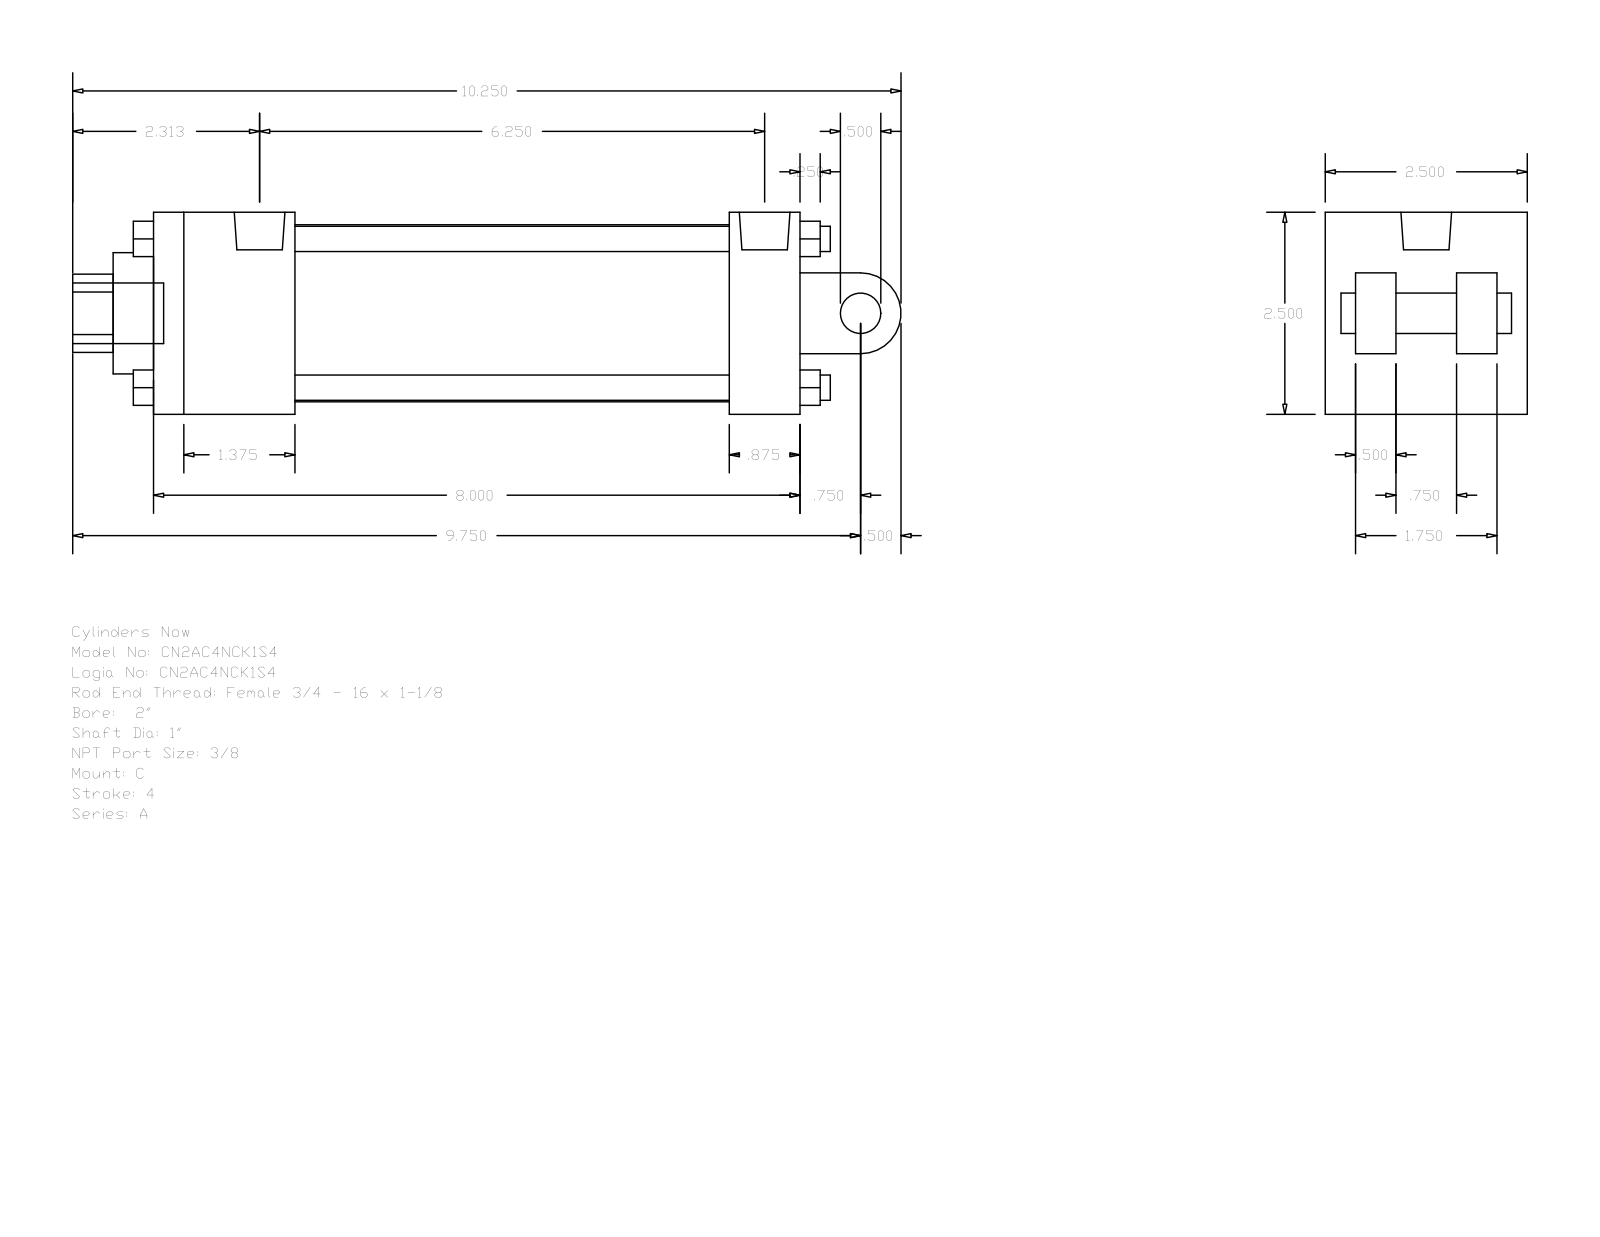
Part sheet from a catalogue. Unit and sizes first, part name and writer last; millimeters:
Units: millimetres
Overall size (bounding box): 260.35 × 63.5 × 63.5
Round holes (diameter × count): ⌀5.56 ×2, ⌀15.93 ×1, ⌀25.4 ×1, ⌀38.1 ×1, ⌀55.63 ×1
Round bosses / shafts (diameter × count): ⌀7.94 ×4, ⌀5.56 ×2, ⌀19.05 ×1, ⌀15.93 ×1, ⌀12.7 ×1
Partial cylindrical surfaces — rounded edges, fillets, slot ends (radius × count): R12.29 ×1, R12.7 ×1
Main face-to-face distances: 63.5, 22.22, 203.2, 44.45, 12.7, 9.52, 41.28, 158.75, 180.98, 136.53
Hole centre spacings: 3.98
Bodies: 0 solids, 135 faces (102 planar, 33 cylindrical, 0 other)
Part name (STEP PRODUCT): A_C__0200_1
STEP written by: GSSL Pune (CONFIG_CONTROL_DESIGN)
